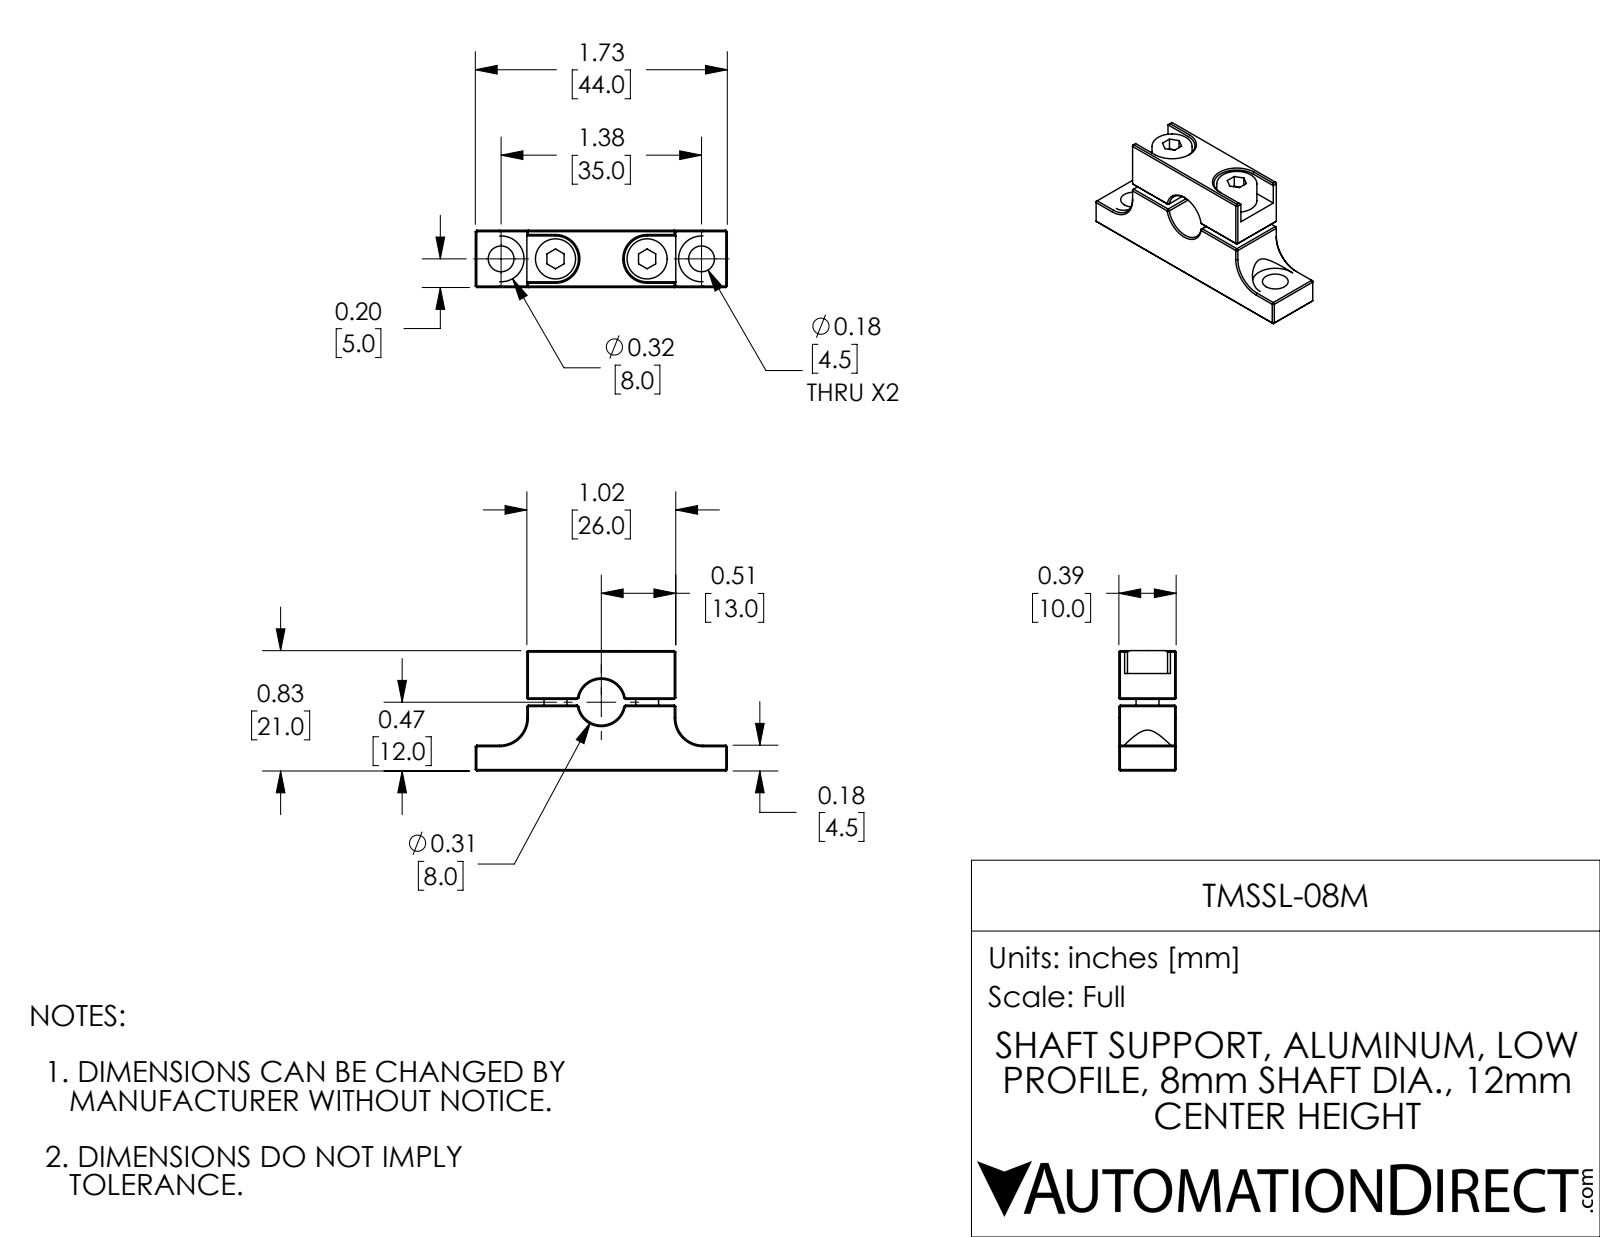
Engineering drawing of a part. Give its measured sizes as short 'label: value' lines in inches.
name: TMSSL-08M
written by: SolidWorks 2017 (AUTOMOTIVE_DESIGN)
unit: in
bodies: 4 solids, 185 faces (114 planar, 33 cylindrical, 38 other)
size: 1.732 × 0.827 × 0.394
volume: 0.315 in³; area: 6.151 in²
holes: 4× ⌀0.177, 2× ⌀0.128, 1× ⌀0.315
bosses: 2× ⌀0.276, 2× ⌀0.157
rounds: 4× R0.158, 2× R0.187
face distances: 0.394, 0.039, 0.354, 0.315, 0.67, 0.453, 0.217, 0.492, 0.178, 0.827
hole spacings: 0.374, 1.004, 0.63, 1.378
